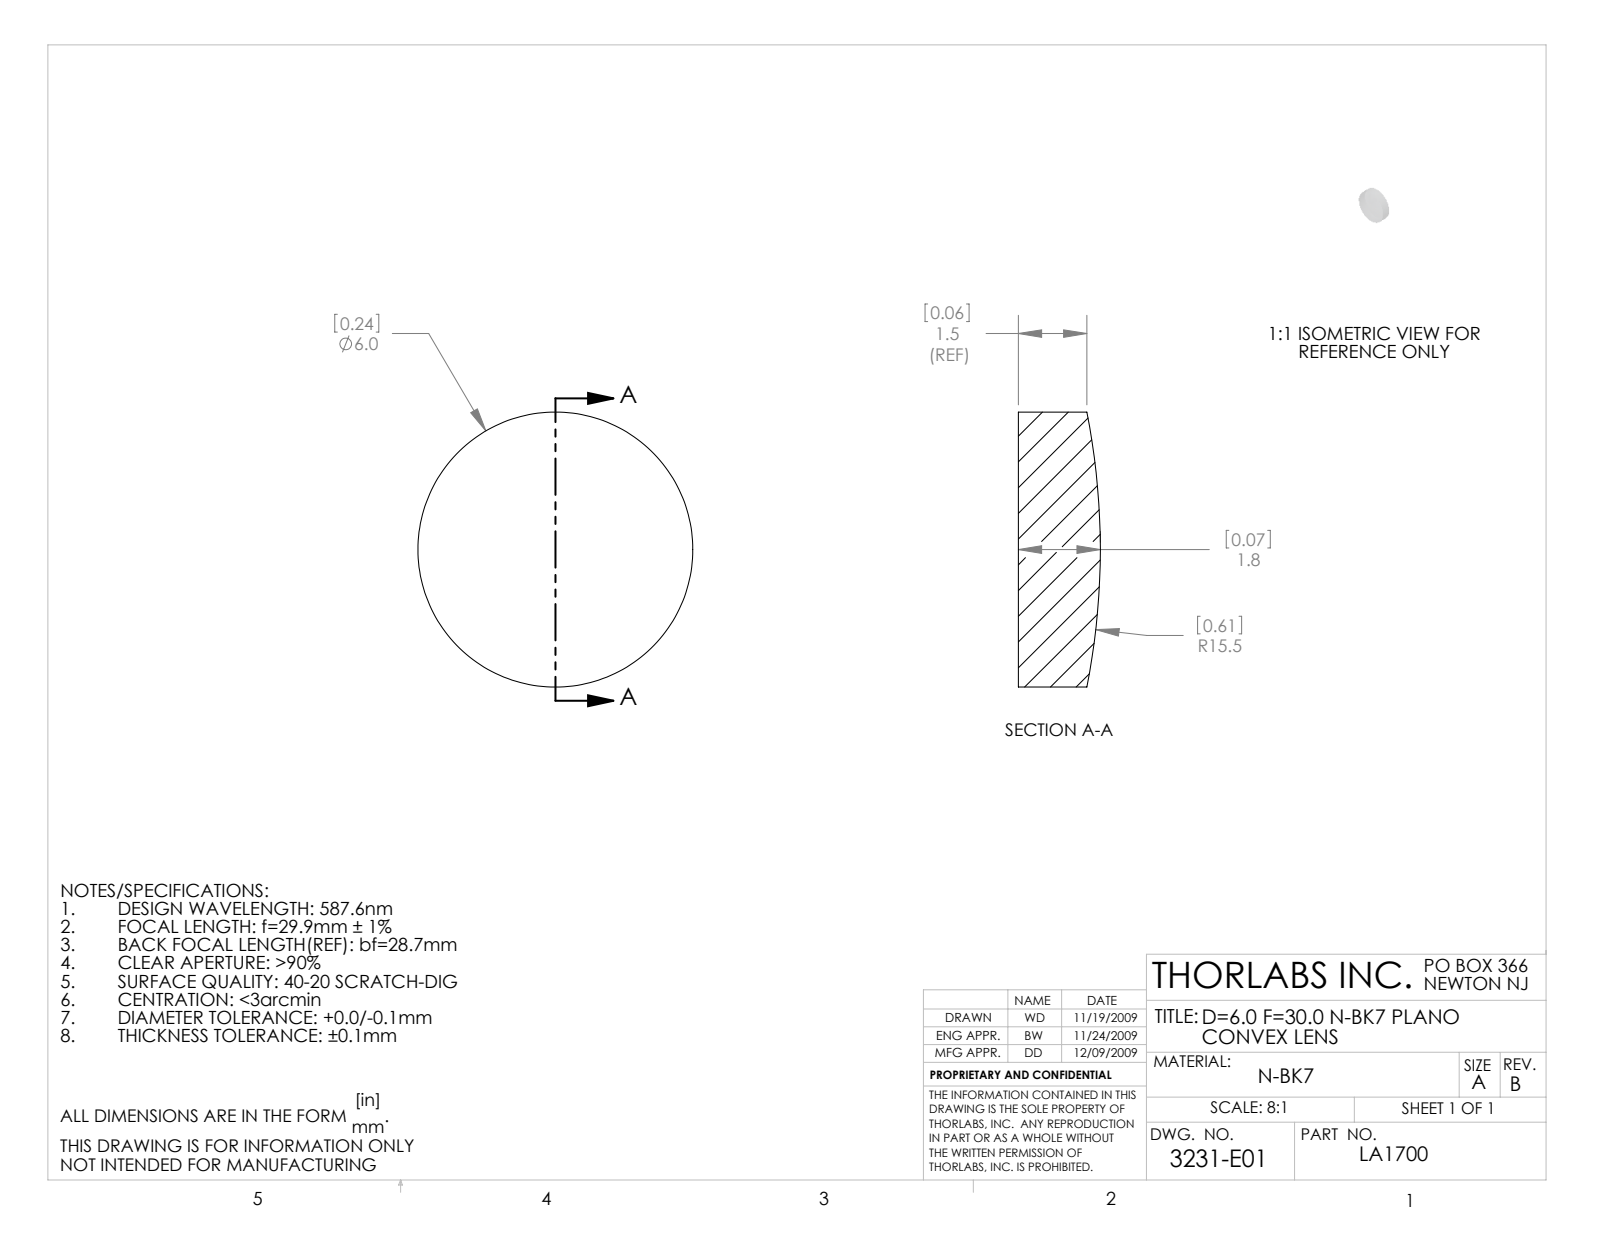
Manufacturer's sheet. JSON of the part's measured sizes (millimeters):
{"part_name": "3231-E0W", "step_written_by": "SolidWorks 2009 (AUTOMOTIVE_DESIGN)", "units": "millimeters", "bodies": {"solids": 1, "faces": 5, "planar": 1, "cylindrical": 2, "other": 2}, "overall_size": [6, 6, 1.79], "volume_mm3": 46, "surface_area_mm2": 85, "round_bosses_or_shafts": [[6, 1]]}
